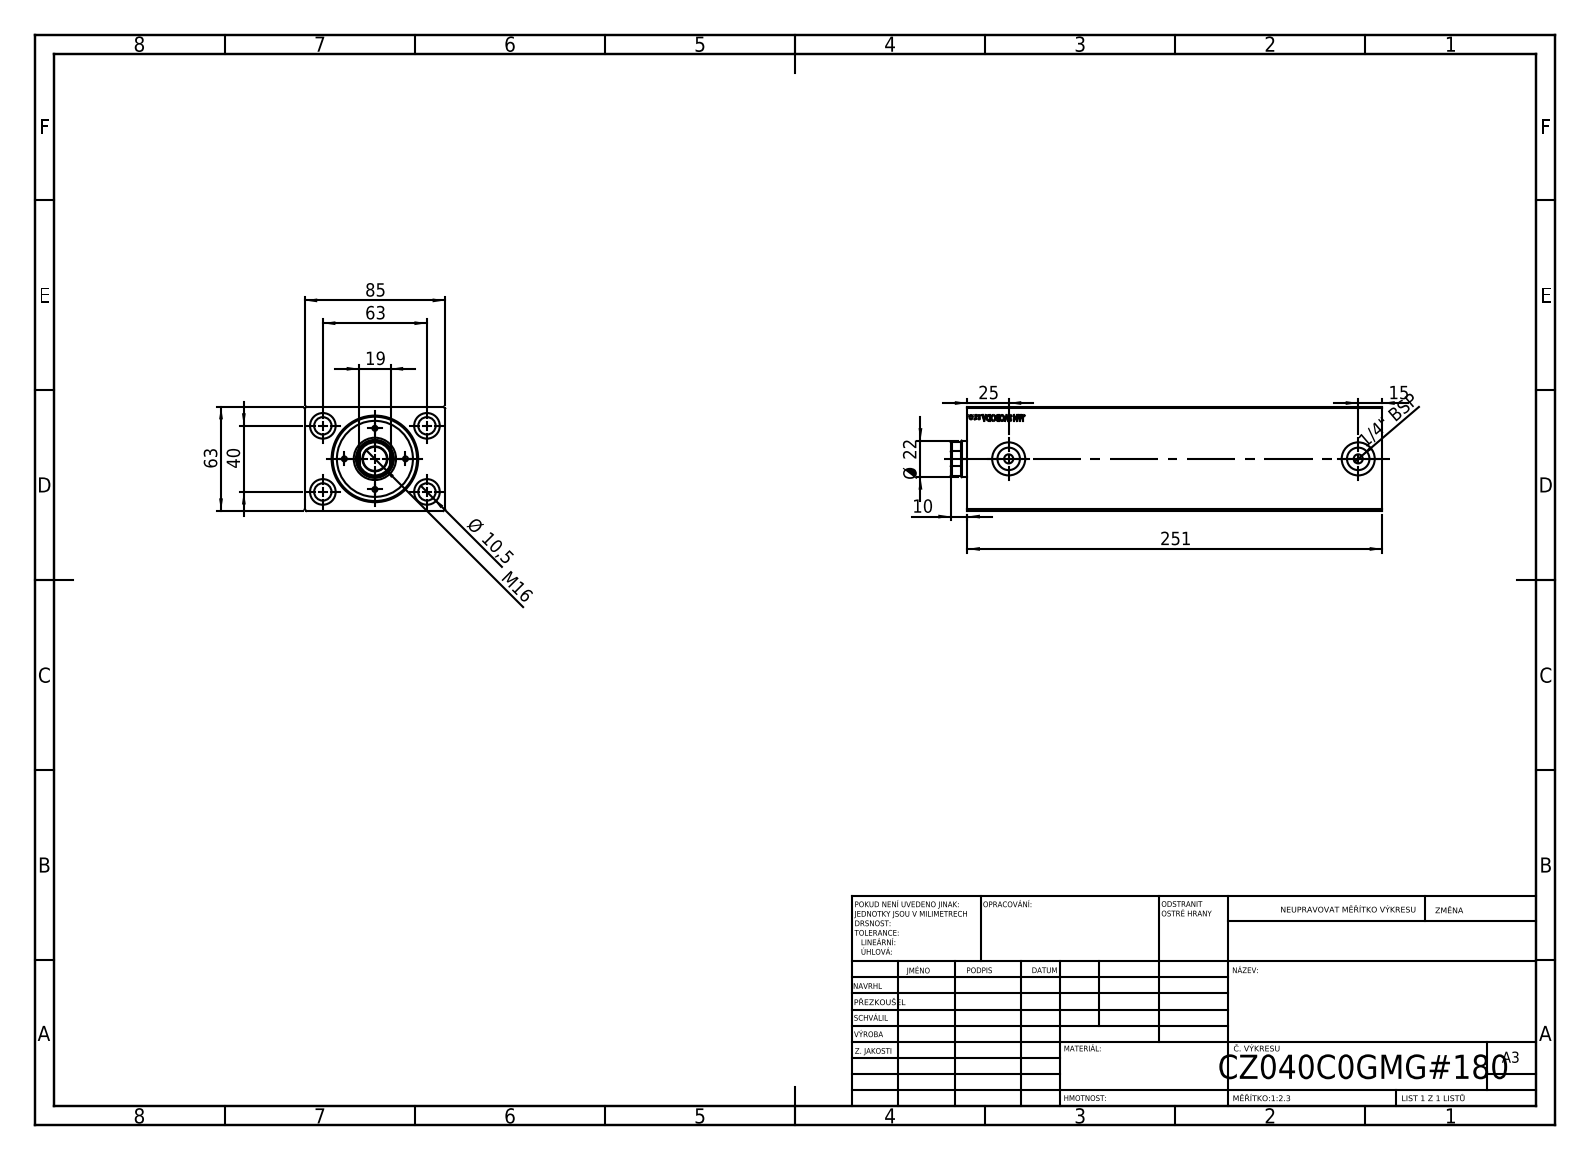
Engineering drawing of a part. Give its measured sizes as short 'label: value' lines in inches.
written by: SolidWorks 2019 (CONFIG_CONTROL_DESIGN)
unit: in
bodies: 1 solid, 825 faces (397 planar, 46 cylindrical, 382 other)
size: 9.882 × 3.346 × 2.48
volume: 57.34 in³; area: 232 in²
holes: 4× ⌀0.413, 4× ⌀0.61, 2× ⌀0.217, 2× ⌀0.315, 2× ⌀0.535, 2× ⌀0.787, 1× ⌀1.417, 1× ⌀1.575, 1× ⌀2.008
face distances: 2.48, 3.346, 9.882, 9.28, 0.602, 9.874, 0.594, 0.407, 9.475, 0.394
hole spacings: 1.469, 1.575, 2.48, 2.938, 7.539, 8.327
